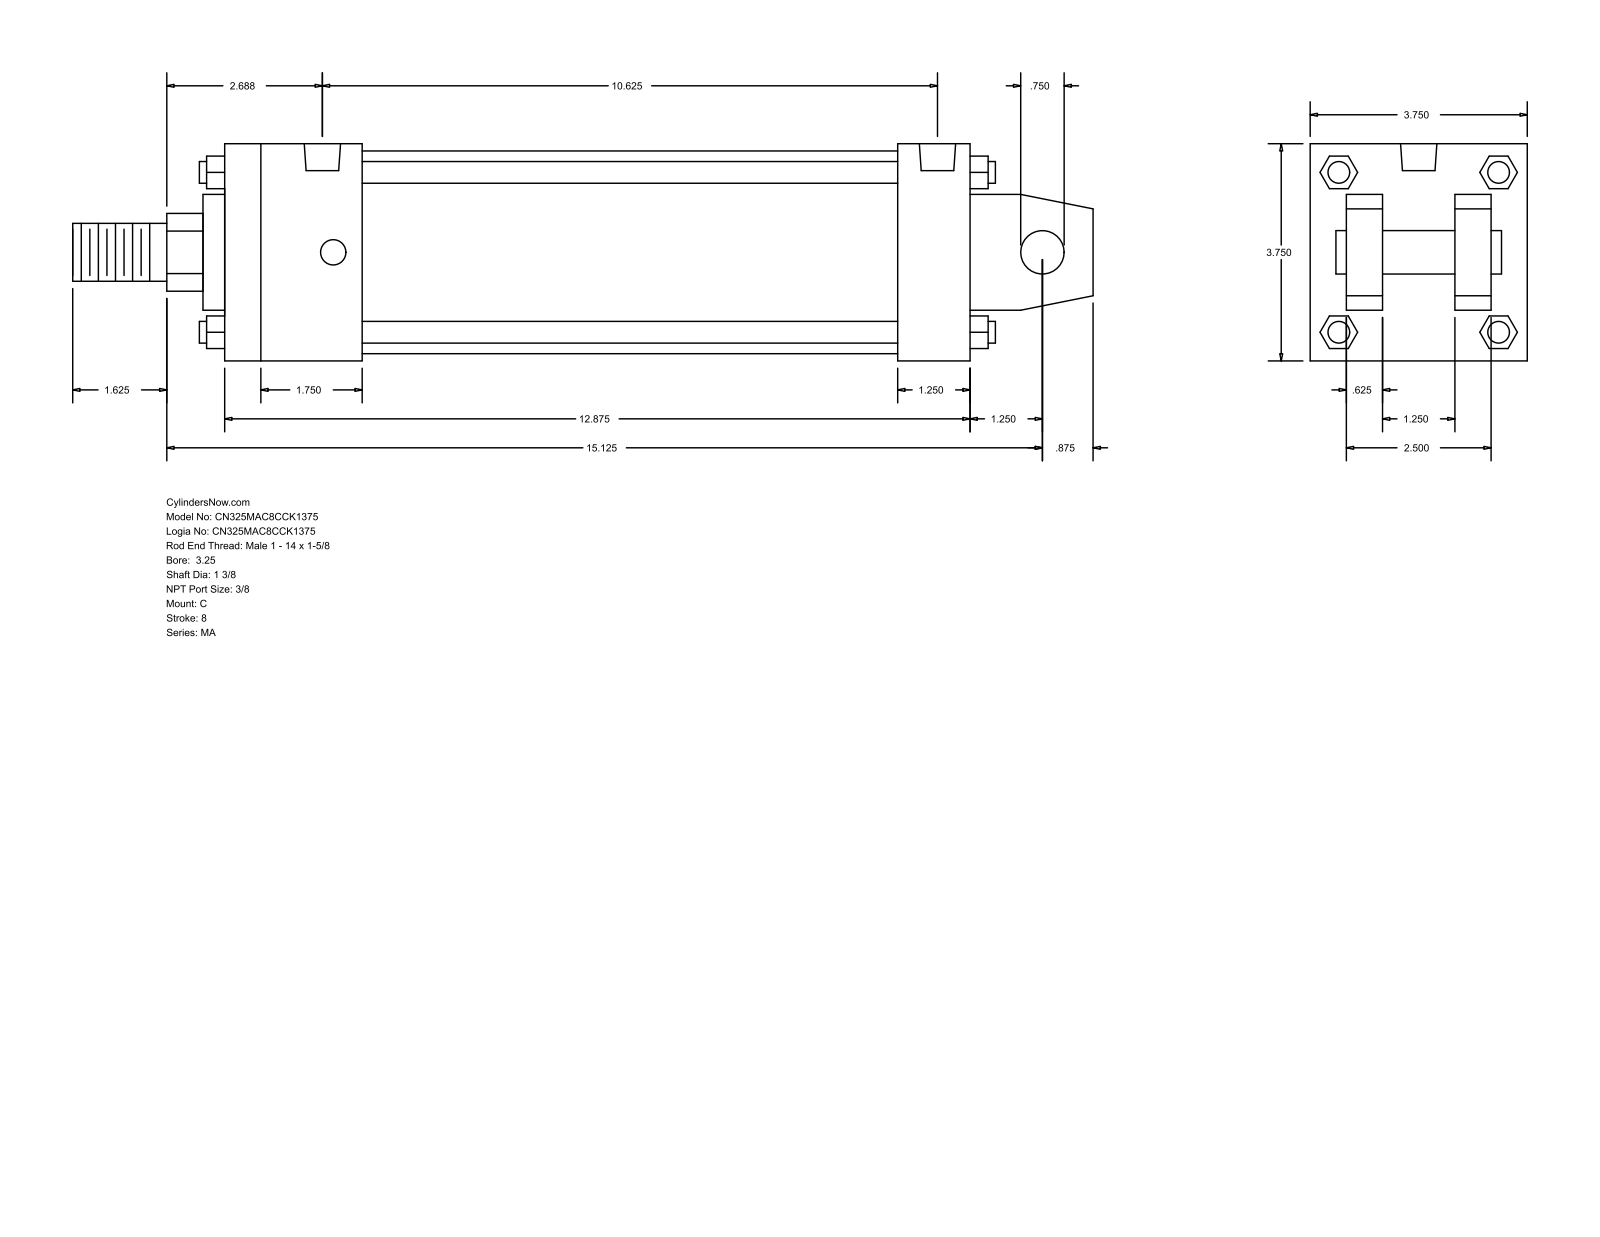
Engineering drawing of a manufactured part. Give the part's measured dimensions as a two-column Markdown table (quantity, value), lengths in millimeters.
| quantity | value |
| --- | --- |
| part name | MA_C__0325_1.375 |
| STEP written by | GSSL Pune (CONFIG_CONTROL_DESIGN) |
| units | millimeters |
| bodies | 0 solids, 139 faces (108 planar, 31 cylindrical, 0 other) |
| overall size | 447.68 × 95.25 × 95.25 |
| round holes (diameter × count) | 11.11 × 4, 15.93 × 2 |
| round bosses / shafts (diameter × count) | 9.53 × 4, 88.9 × 1, 50.8 × 1, 34.92 × 1, 25.4 × 1, 19.05 × 1 |
| partial cylindrical surfaces (radius × count) | 17.06 × 1 |
| main face-to-face distances | 95.24, 15.87, 63.5, 327.03, 31.74, 79.37, 47.63, 295.28, 31.75, 60.32 |
| hole center spacings | 260.35, 4.76, 4.77, 265.11, 265.12, 269.88 |
